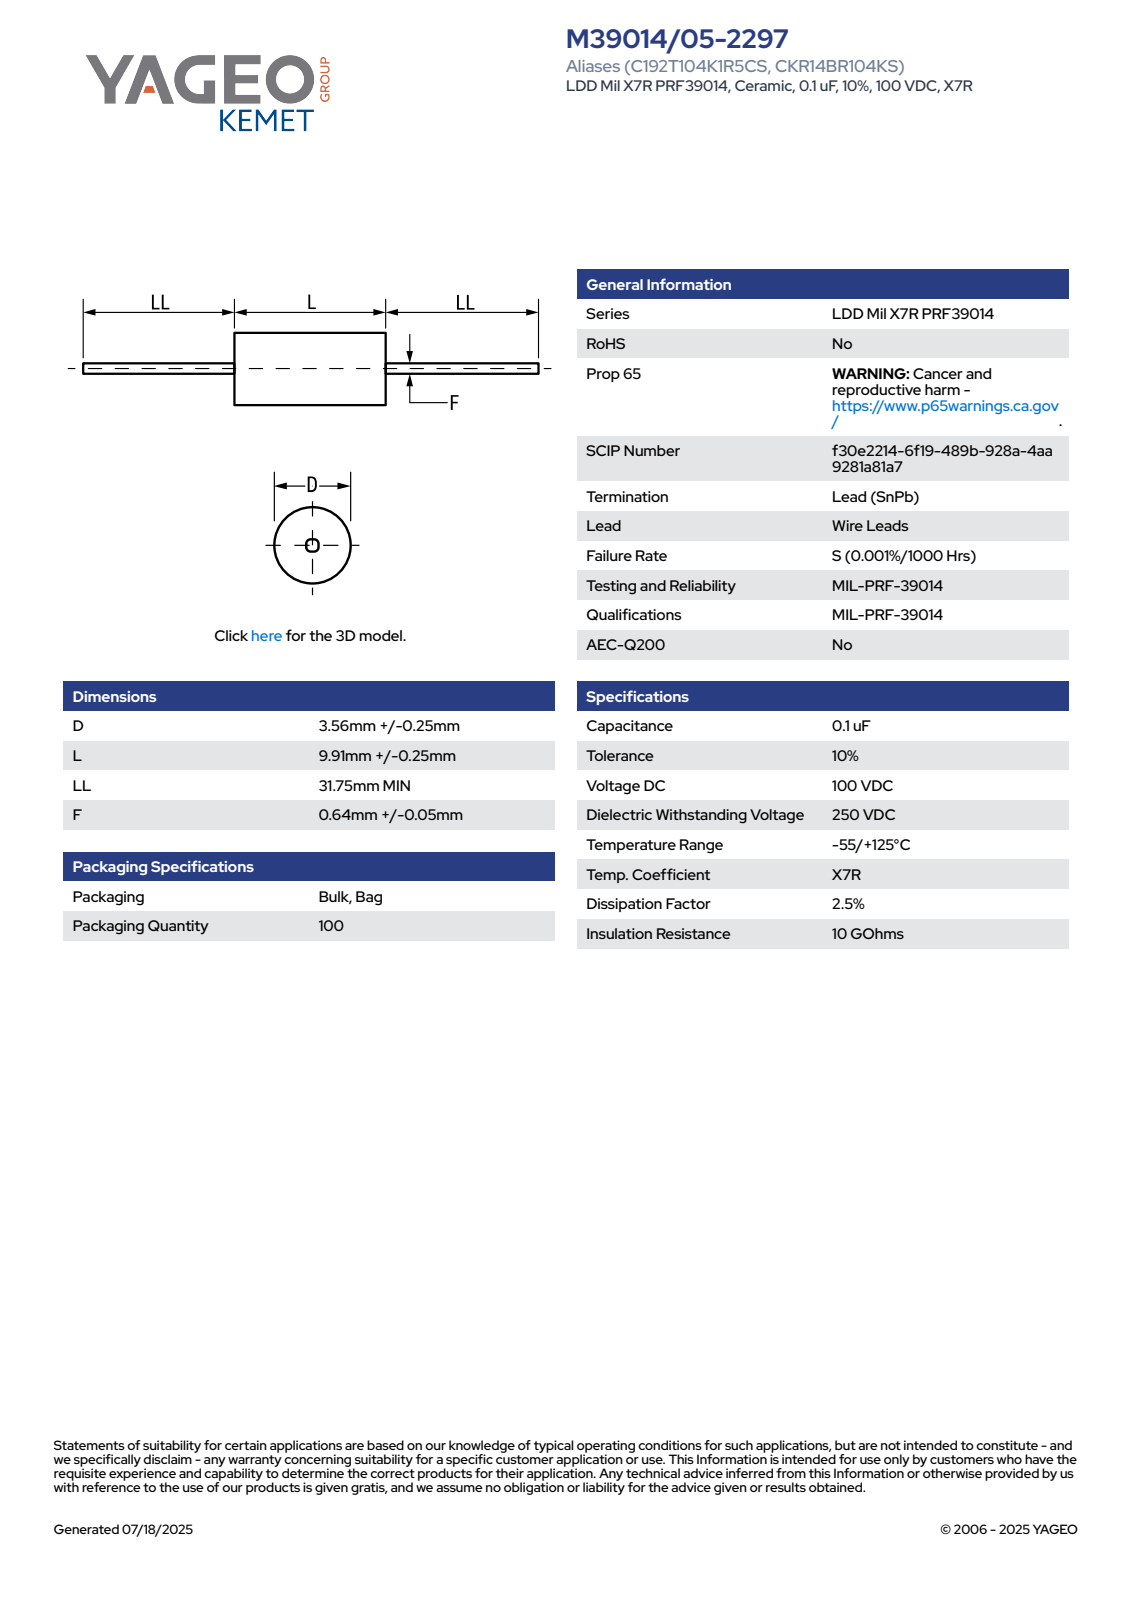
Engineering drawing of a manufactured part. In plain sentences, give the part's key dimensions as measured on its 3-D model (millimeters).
The part is named "CCA_AXM_C192_D3.81L10.16LL38.1F0.69". Its 3-D file was written by "SolidWorks 2014 (AUTOMOTIVE_DESIGN)". It is 1 solid with 66 faces: 26 planar, 9 cylindrical and 31 other. Overall it measures 86.36 by 3.81 by 3.81 millimeters. Its volume is 144 cubic millimeters and its surface area 310 square millimeters. Round bosses or shafts: 1 of diameter 3.81, 1 of diameter 0.69. Partial cylindrical surfaces (rounded edges, fillets, slot ends): 1 of radius 1.9. The main face-to-face distances are 10.16, 38.1, 48.26, 86.36.
